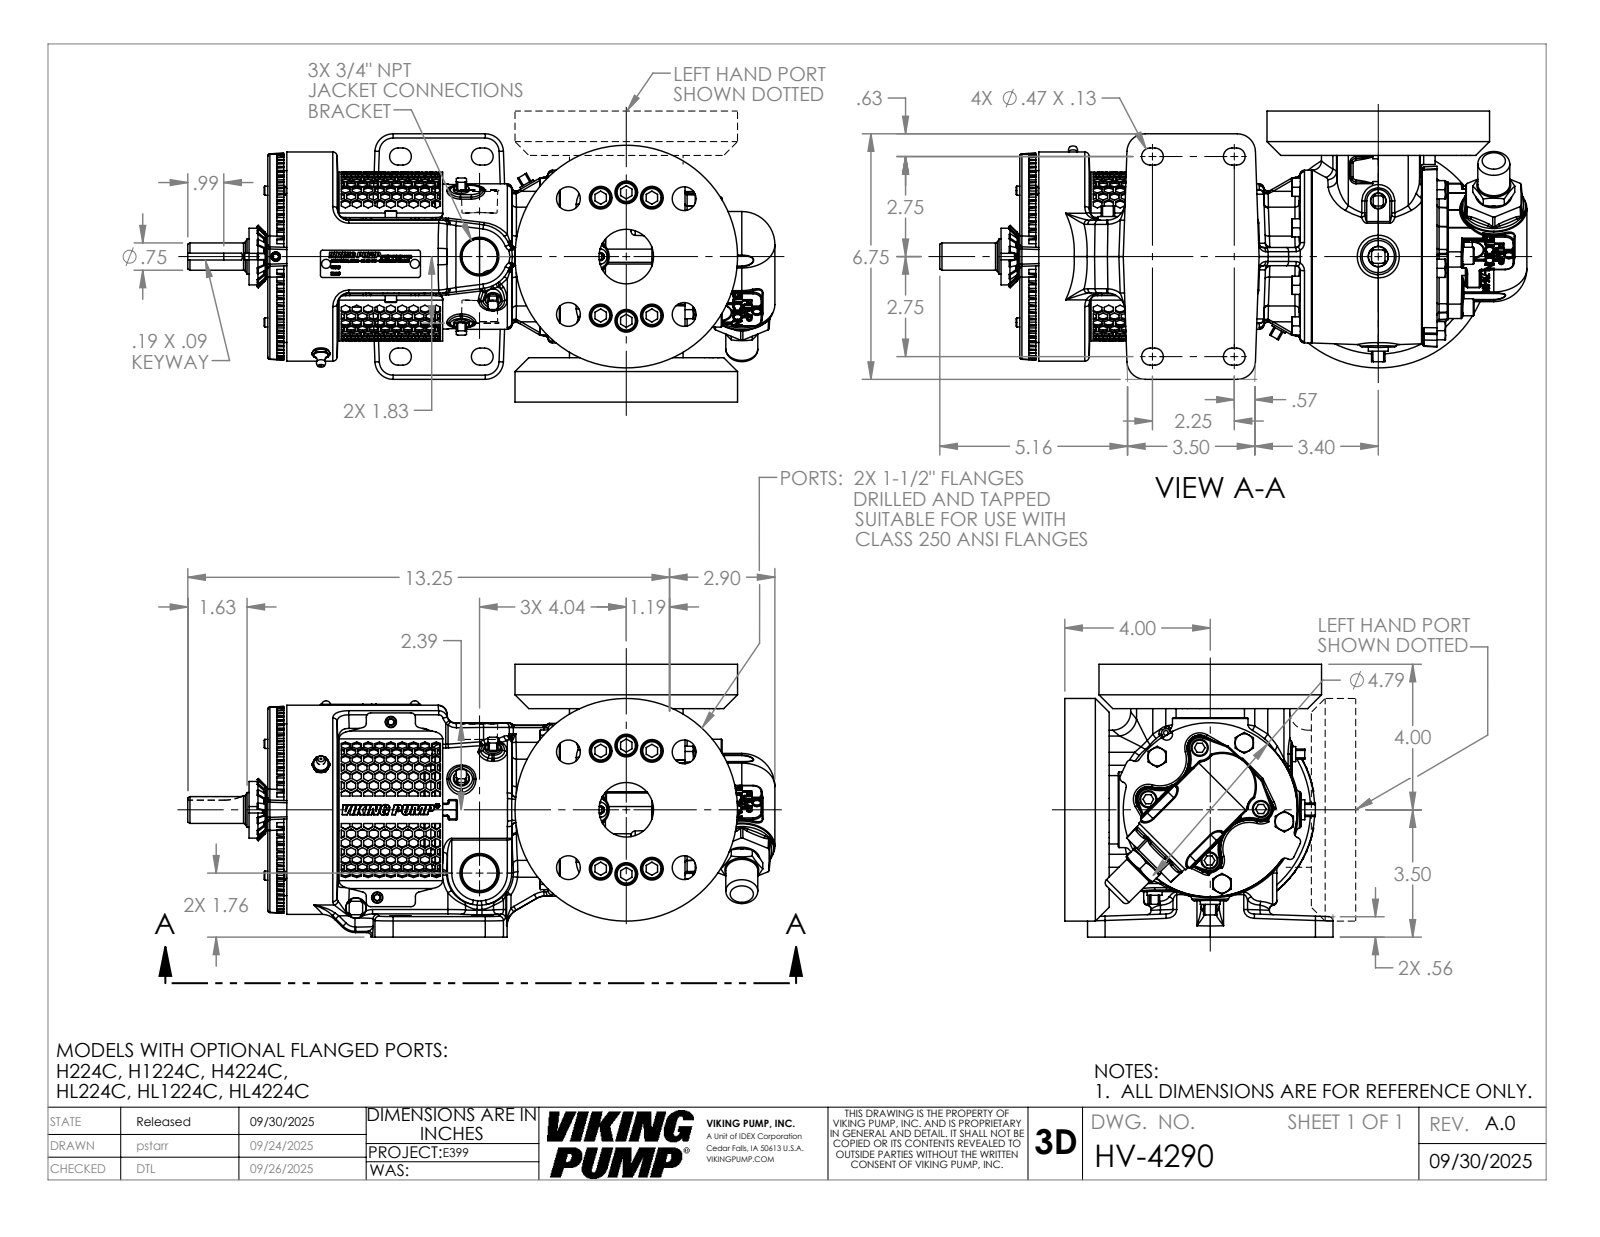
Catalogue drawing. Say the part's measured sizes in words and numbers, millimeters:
The part is named "HV-4290". Its 3-D file was written by "SolidWorks 2024 (AUTOMOTIVE_DESIGN)". It is 1 solid with 5265 faces: 1873 planar, 1012 cylindrical and 2380 other. Overall it measures 410.08 by 190.5 by 187.32 millimeters. Its volume is 4 492 000 cubic millimeters and its surface area 444 333 square millimeters. Round holes: 9 of diameter 6.35, 8 of diameter 15.88, 8 of diameter 16.67, 4 of diameter 8.64, 4 of diameter 8.74, 4 of diameter 15.87, 3 of diameter 4.04, 3 of diameter 5.02, 2 of diameter 6.53, 2 of diameter 38.1, 1 of diameter 25.03, 1 of diameter 25.12. Round bosses or shafts: 12 of diameter 14.29, 4 of diameter 11.91, 4 of diameter 7.95, 3 of diameter 7.92, 3 of diameter 4.83, 2 of diameter 155.45, 2 of diameter 6.35, 1 of diameter 146.05. Partial cylindrical surfaces (rounded edges, fillets, slot ends): 140 of radius 1.37, 94 of radius 0.76, 85 of radius 3.05, 56 of radius 1.52, 40 of radius 12.7, 10 of radius 6.35, 8 of radius 5.95, 8 of radius 9.65. The main face-to-face distances are 190.5, 30.99, 49.28, 159.51, 291.43, 242.15, 38.1, 13.3, 35.98, 278.13. The hole center spacings are 44.85, 65.03, 18.26, 22.54, 40.65, 57.15, 58.29, 80.82.
